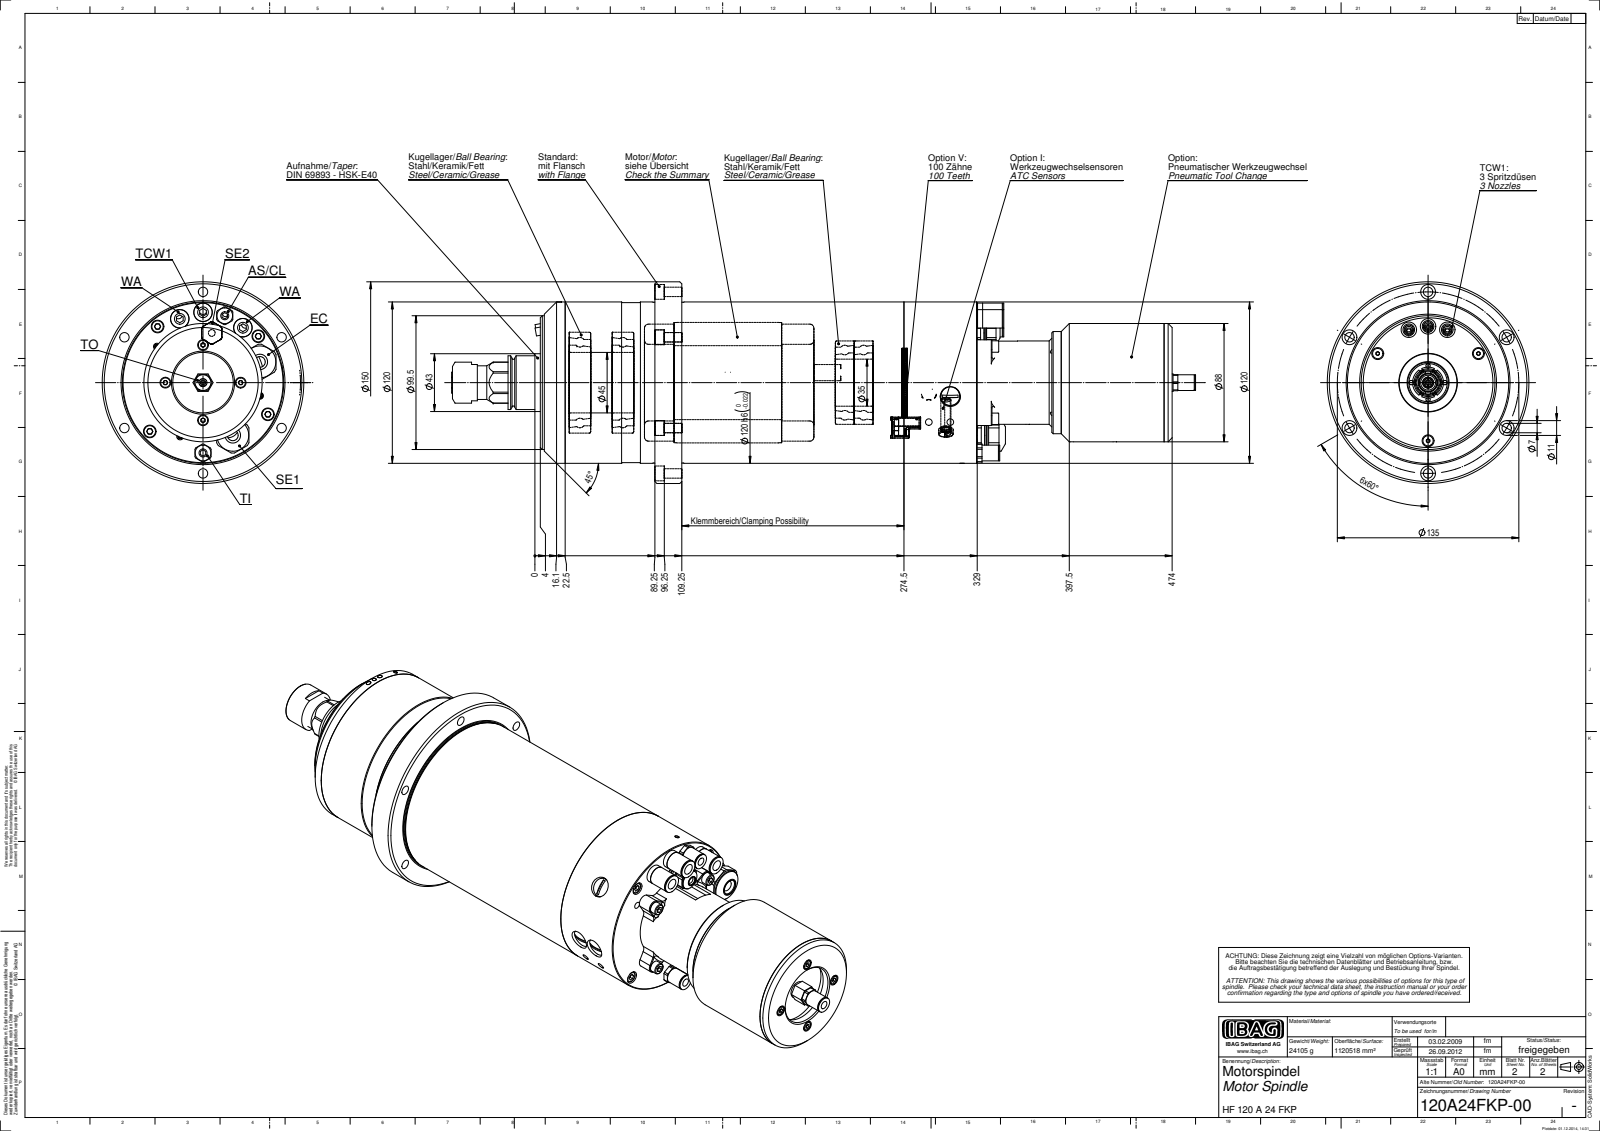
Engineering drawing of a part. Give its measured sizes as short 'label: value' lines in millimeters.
name: 120A24FKP-00
written by: SolidWorks 2012 (CONFIG_CONTROL_DESIGN)
unit: mm
bodies: 0 solids, 809 faces (291 planar, 332 cylindrical, 186 other)
size: 553.38 × 150 × 150
holes: 9× ⌀8, 6× ⌀5, 6× ⌀7, 6× ⌀11, 5× ⌀6, 5× ⌀11.5, 5× ⌀15, 4× ⌀4.2, 4× ⌀9.4, 4× ⌀10, 3× ⌀2.5, 3× ⌀4.5
bosses: 4× ⌀8.5, 3× ⌀13.7, 3× ⌀11.7, 3× ⌀7.64, 3× ⌀7, 3× ⌀6, 2× ⌀23.7, 2× ⌀22.3
rounds: 14× R5, 3× R6.6, 2× R13.2, 1× R8.25, 1× R10
face distances: 306.5, 54.5, 252, 325, 369, 117, 62.5, 18.5, 20, 445.5
hole spacings: 67.5, 116.92, 34, 53.7, 61.33, 104.03, 17.48, 35.76
